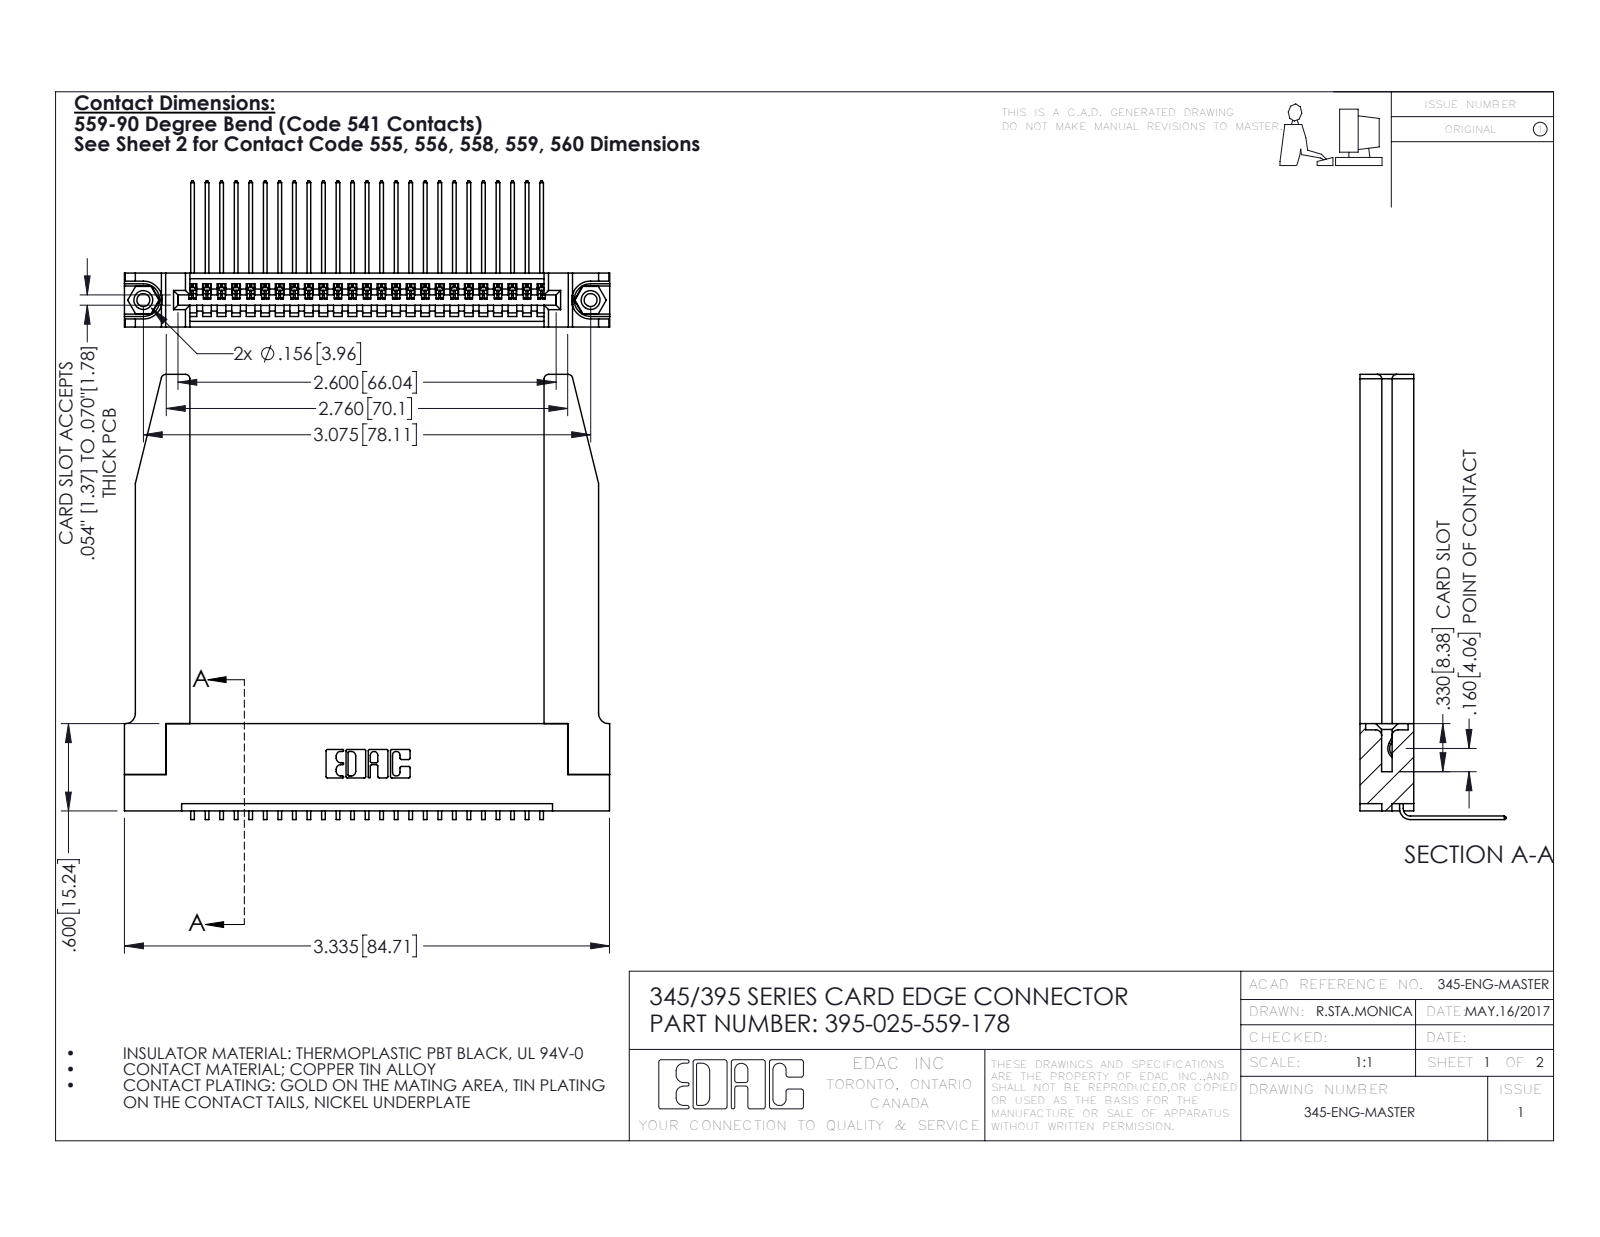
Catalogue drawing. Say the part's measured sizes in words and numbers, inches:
The part is named "345-292-001_558 559 Tail - 1; 345-220-078_345-220-078; 345-250-001_345-250-001-102; 395-025-559-178 (+1 more)". Its 3-D file was written by "SolidWorks 2016 (CONFIG_CONTROL_DESIGN)". It is 30 solids with 1860 faces: 1272 planar, 536 cylindrical and 52 other. Overall it measures 3.336 by 3.059 by 1.005 inches. Its volume is 0.962 cubic inches and its surface area 27.47 square inches. Round holes: 2 of diameter 0.089, 2 of diameter 0.125, 2 of diameter 0.156, 1 of diameter 0.064. Round bosses or shafts: 2 of diameter 0.155. Partial cylindrical surfaces (rounded edges, fillets, slot ends): 50 of radius 0.006, 22 of radius 0.01, 8 of radius 0.03, 6 of radius 0.007, 6 of radius 0.031, 3 of radius 0.026, 2 of radius 0.031, 2 of radius 0.04. The main face-to-face distances are 0.37, 0.072, 0.298, 0.2, 0.098, 0.272, 0.025, 0.148, 0.15, 0.225. The hole center spacings are 0.27, 2.84, 3.075.
